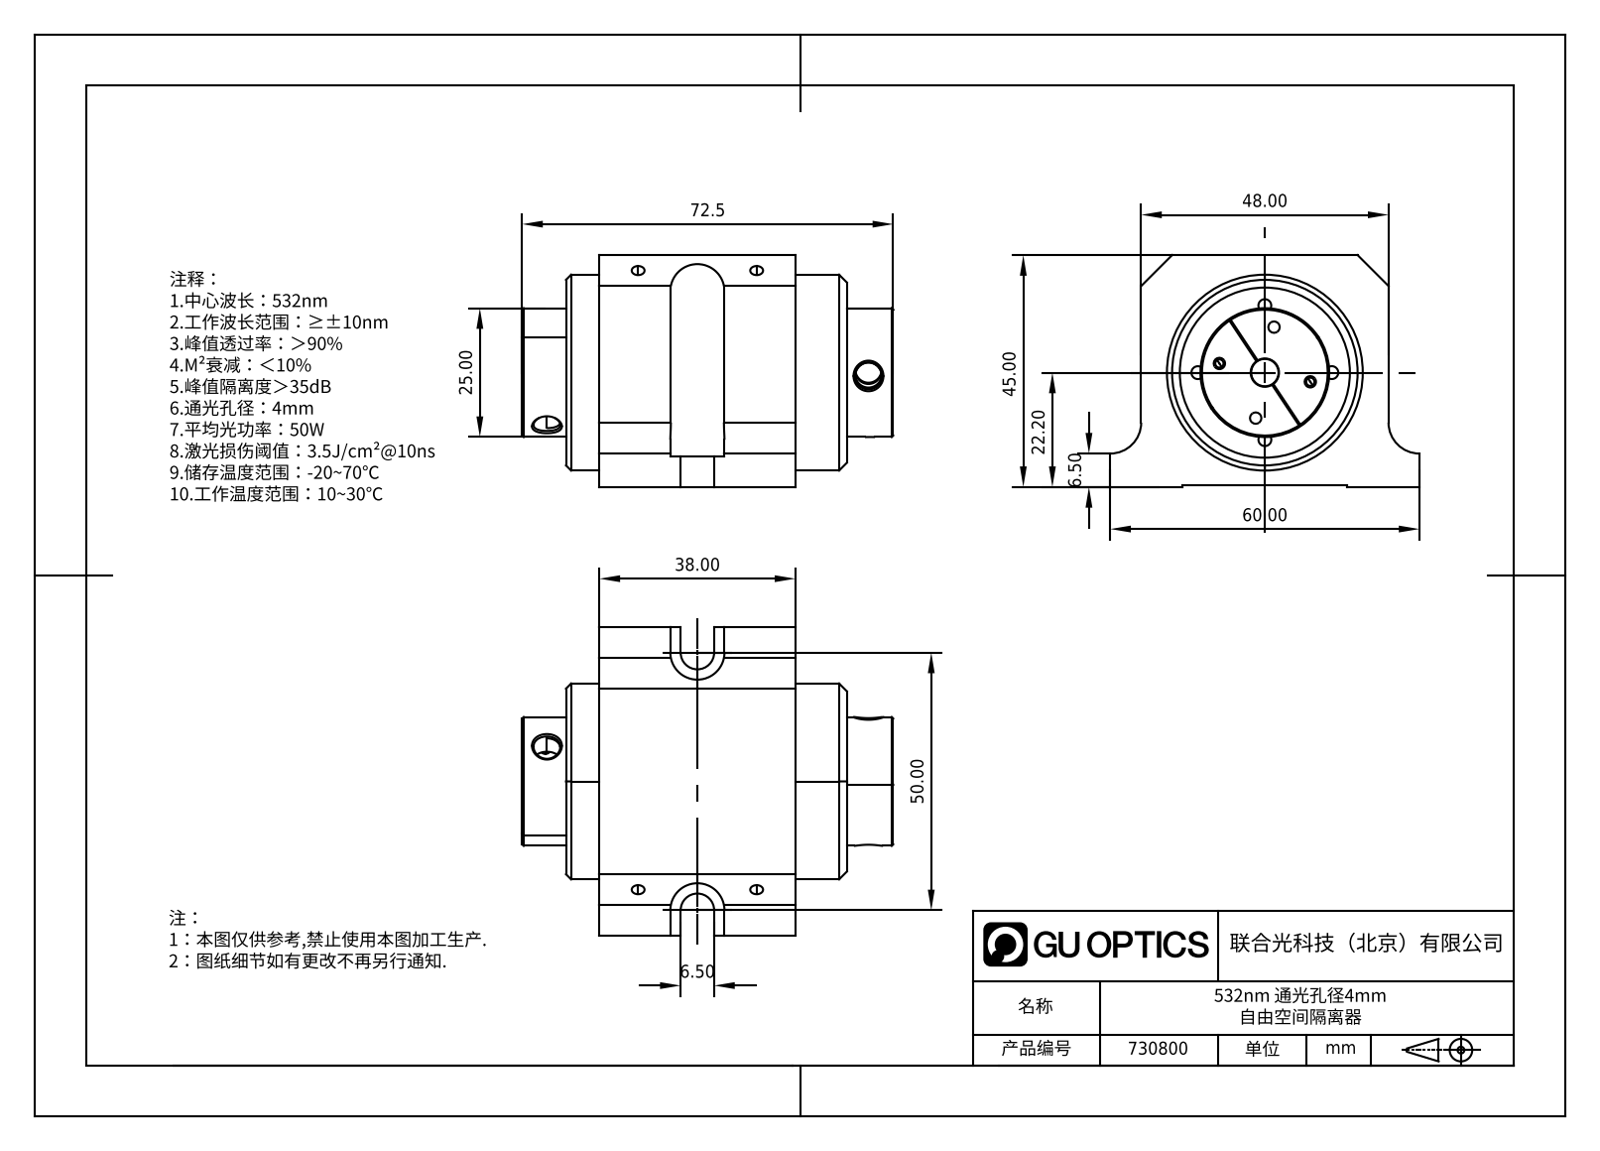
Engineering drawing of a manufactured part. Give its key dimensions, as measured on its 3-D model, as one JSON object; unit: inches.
{"part_name": "730800", "step_written_by": "SolidWorks 2020 (CONFIG_CONTROL_DESIGN)", "units": "inches", "bodies": {"solids": 1, "faces": 289, "planar": 88, "cylindrical": 145, "other": 56}, "overall_size": [2.835, 2.362, 1.772], "volume_in3": 4.055, "surface_area_in2": 39.42, "round_holes": [[0.087, 11], [0.063, 10], [0.098, 6], [0.118, 2], [0.205, 2], [0.201, 1], [0.209, 1], [0.217, 1], [0.315, 1], [0.551, 1], [0.787, 1], [0.866, 1]], "round_bosses_or_shafts": [[1.496, 1], [1.331, 1], [0.984, 1], [0.906, 1], [0.394, 1]], "partial_cylinders_radius": [[0.047, 4], [0.128, 2], [0.207, 2], [0.236, 2]], "face_to_face_distances": [1.89, 1.756, 0.236, 1.496, 0.039, 0.016, 1.772, 2.48, 0.256, 2.244], "hole_center_spacings": [0.362, 0.256, 0.354, 0.802, 0.25, 0.501, 0.512, 0.565]}
